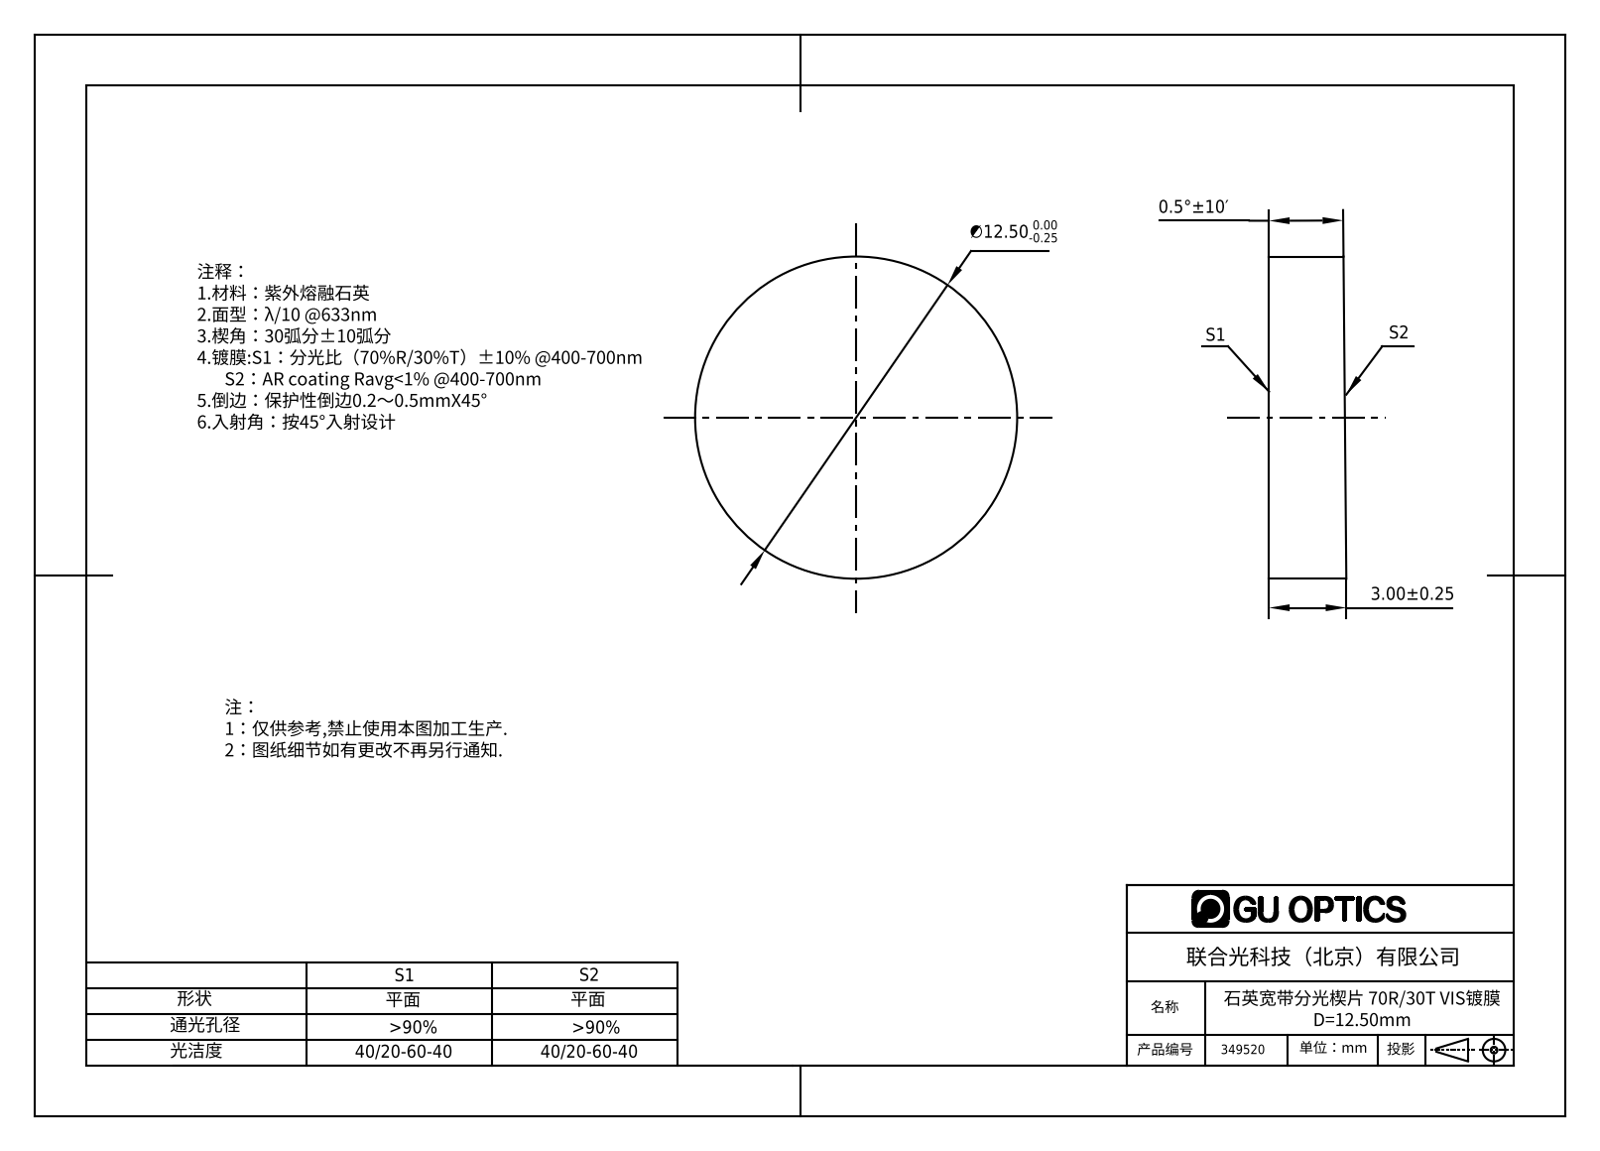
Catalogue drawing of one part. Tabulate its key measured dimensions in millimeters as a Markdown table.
| quantity | value |
| --- | --- |
| part name | 349500 |
| STEP written by | SolidWorks 2016 (AUTOMOTIVE_DESIGN) |
| units | millimeters |
| bodies | 1 solid, 4 faces (2 planar, 2 cylindrical, 0 other) |
| overall size | 12.5 × 12.5 × 3 |
| volume | 361 mm³ |
| surface area | 361 mm² |
| round bosses / shafts (diameter × count) | 12.5 × 1 |
